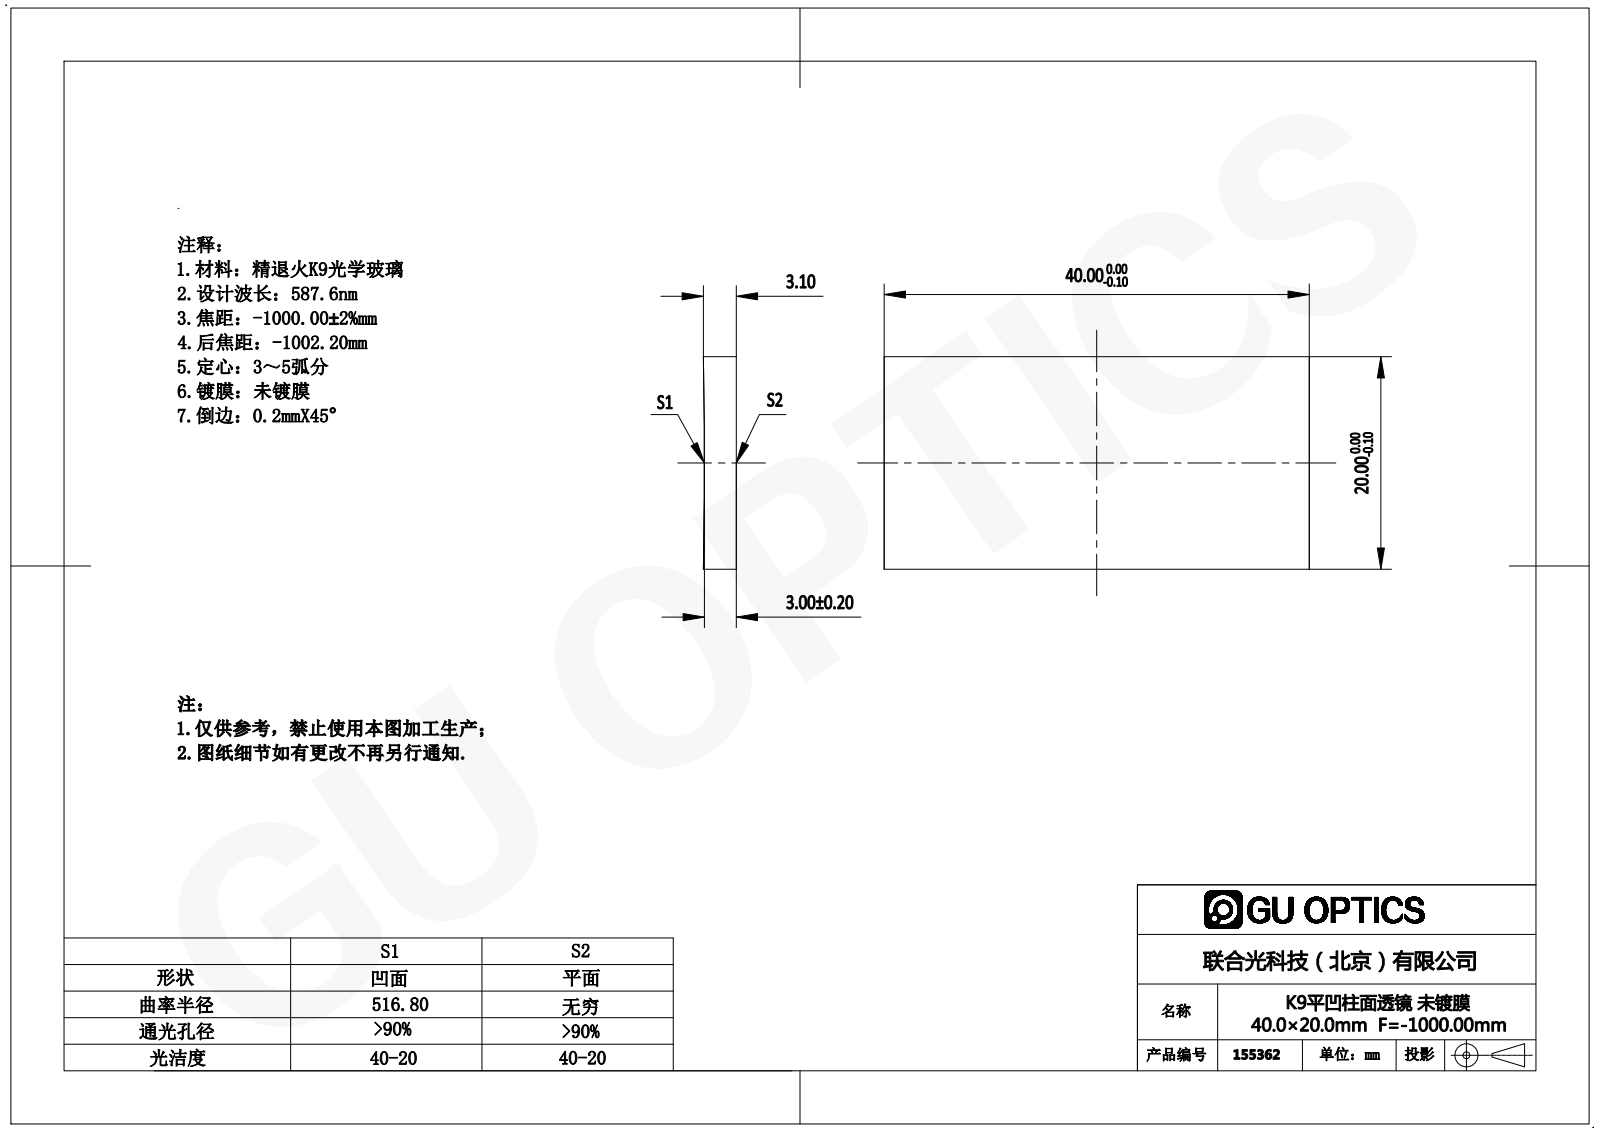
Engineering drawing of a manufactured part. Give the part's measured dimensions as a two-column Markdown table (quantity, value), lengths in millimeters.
| quantity | value |
| --- | --- |
| part name | 155362 |
| STEP written by | SolidWorks 2016 (AUTOMOTIVE_DESIGN) |
| units | millimeters |
| bodies | 1 solid, 6 faces (5 planar, 1 cylindrical, 0 other) |
| overall size | 40 × 20 × 3.1 |
| volume | 2 426 mm³ |
| surface area | 1 969 mm² |
| partial cylindrical surfaces (radius × count) | 516.8 × 1 |
| main face-to-face distances | 20, 40 |
